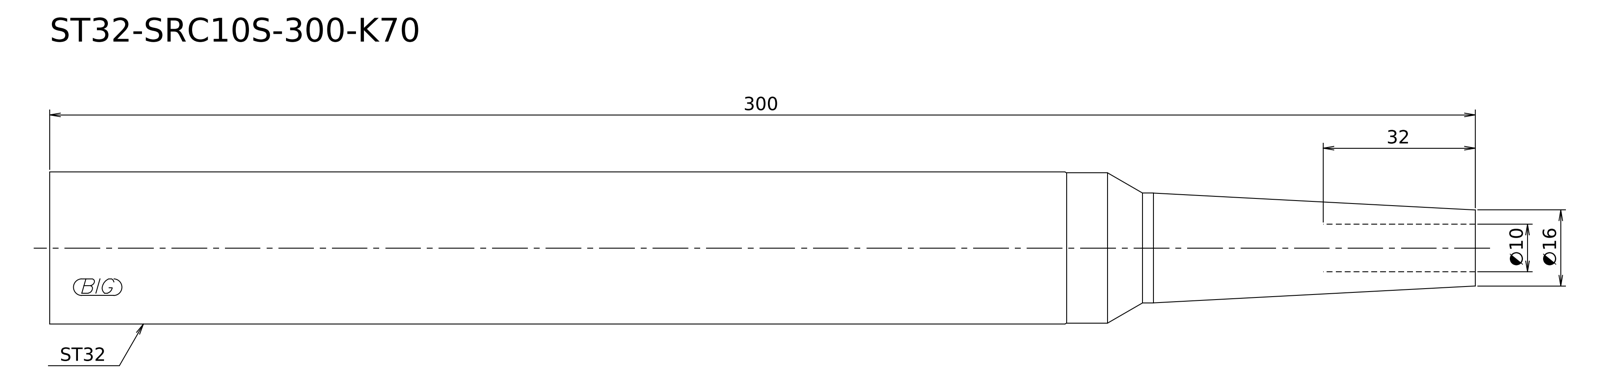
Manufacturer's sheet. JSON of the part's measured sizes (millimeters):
{"step_written_by": "Kubotek KeyCreator V8.5.1 (14335) (CONFIG_CONTROL_DESIGN)", "units": "millimeters", "bodies": {"solids": 1, "faces": 8, "planar": 2, "cylindrical": 3, "other": 3}, "overall_size": [300, 32, 32], "volume_mm3": 204735, "surface_area_mm2": 28442, "round_bosses_or_shafts": [[32, 1], [31.6, 1], [23.1, 1]], "face_to_face_distances": [300]}
